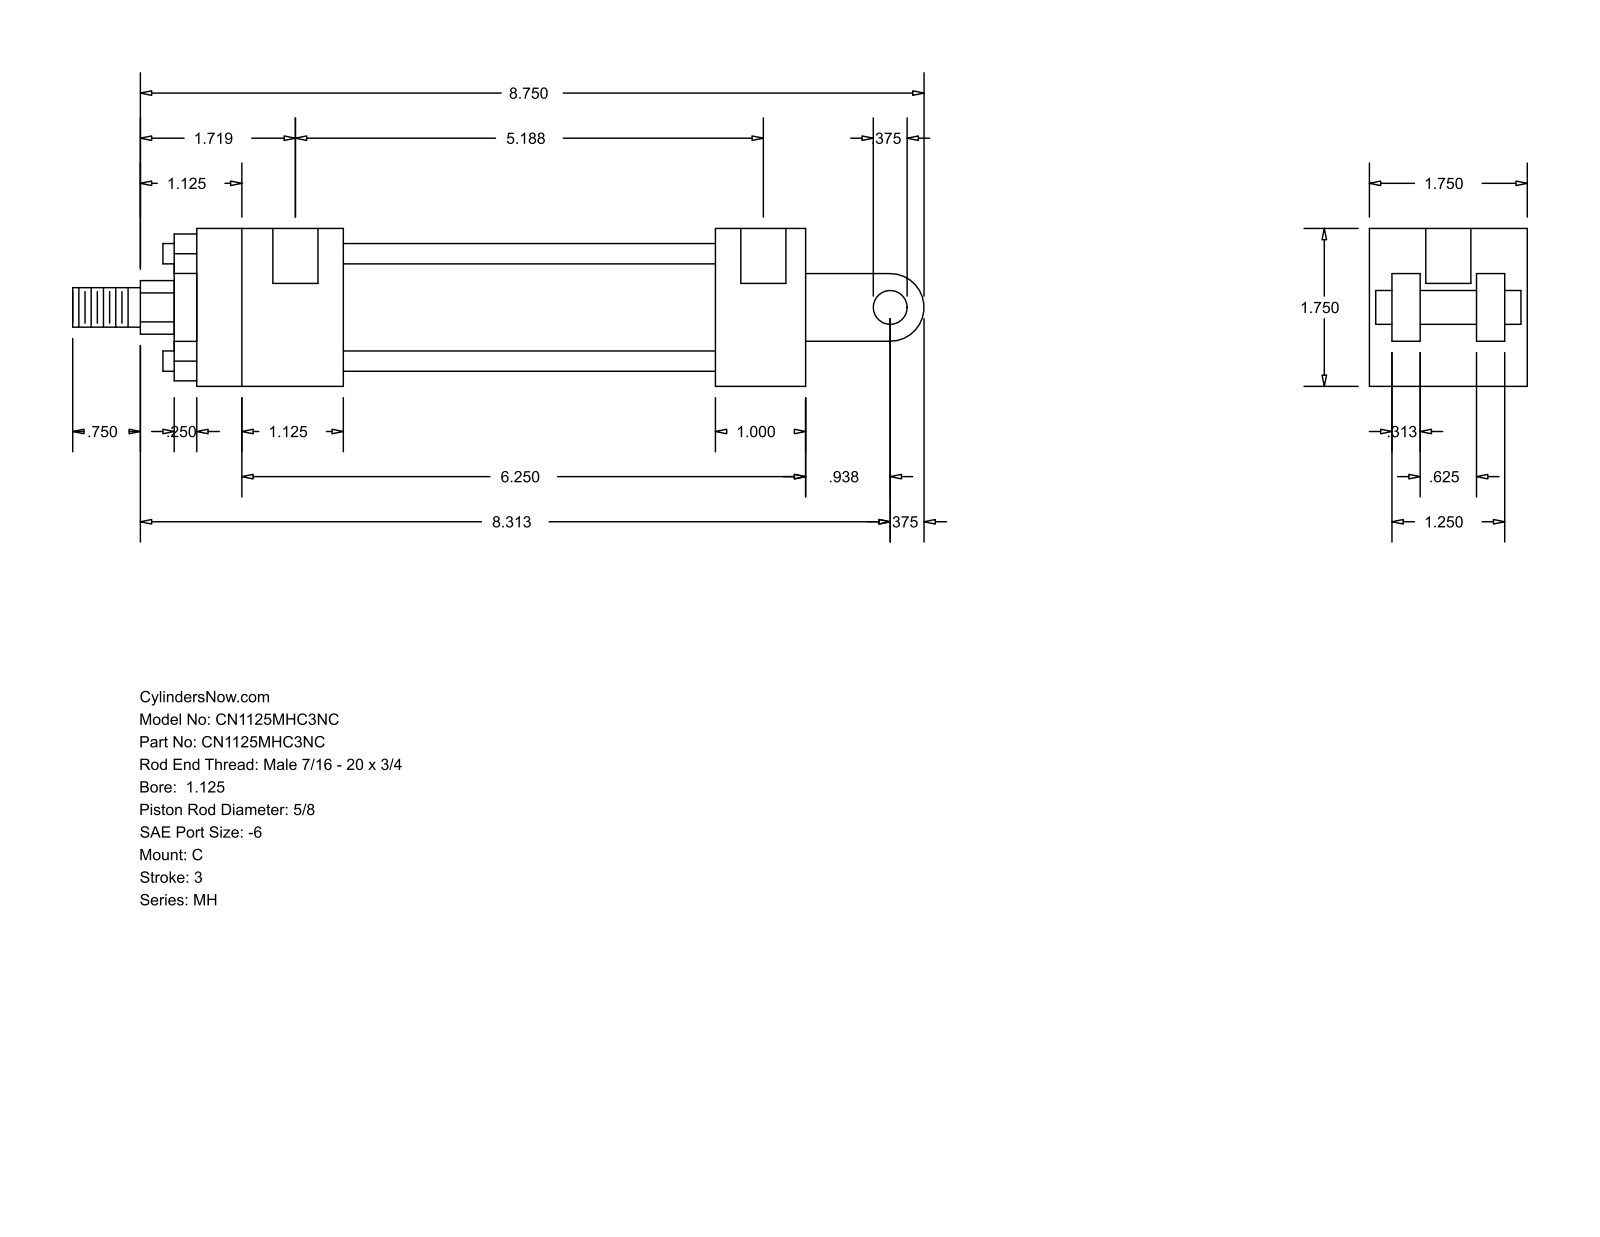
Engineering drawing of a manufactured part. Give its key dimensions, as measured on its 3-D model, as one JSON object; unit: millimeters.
{"part_name": "MH_C__0112_0.625", "step_written_by": "GSSL Pune (CONFIG_CONTROL_DESIGN)", "units": "millimeters", "bodies": {"solids": 0, "faces": 99, "planar": 70, "cylindrical": 29, "other": 0}, "overall_size": [239.71, 44.45, 44.45], "round_holes": [[5.56, 4], [12.7, 2]], "round_bosses_or_shafts": [[5.71, 4], [34.92, 1], [28.57, 1], [15.88, 1], [11.11, 1], [9.53, 1]], "partial_cylinders_radius": [[7.54, 1], [9.53, 1]], "face_to_face_distances": [44.46, 6.35, 31.76, 14.29, 30.17, 38.11, 7.94, 23.82, 41.27, 12.7], "hole_center_spacings": [128.59, 3.17, 131.76]}
